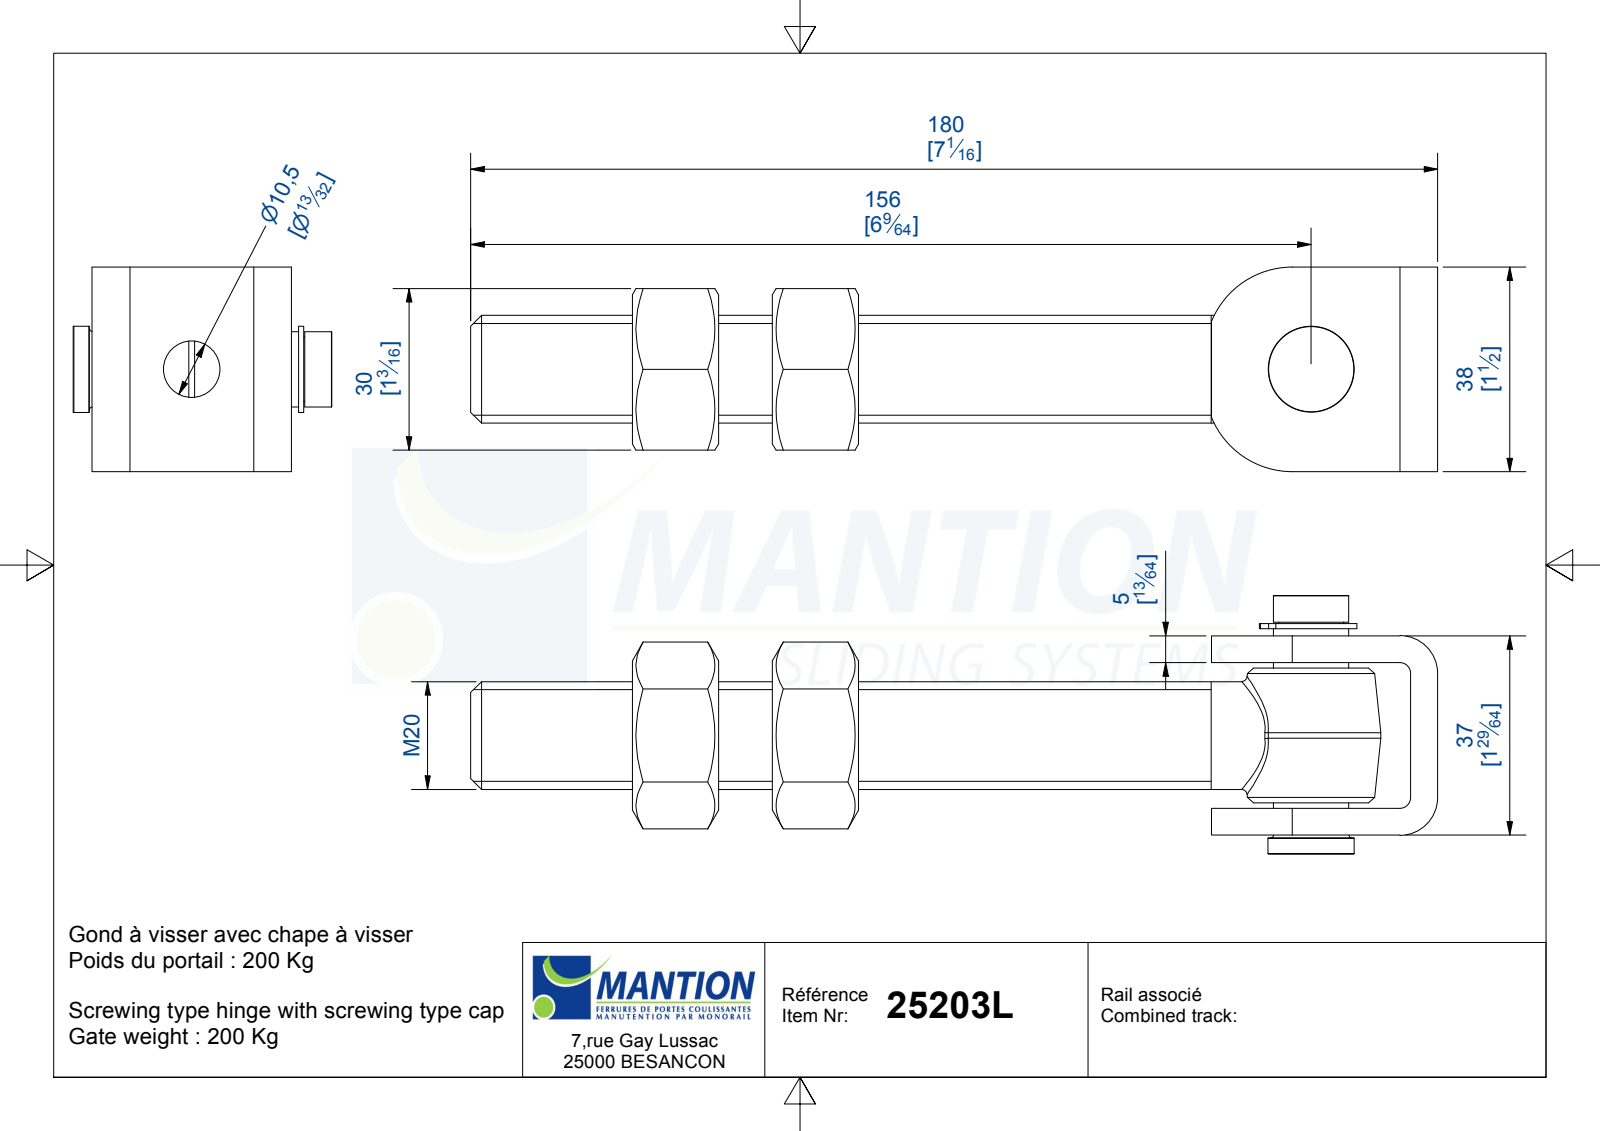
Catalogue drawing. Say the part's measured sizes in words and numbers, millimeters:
The part is named "25203L; 25203-2; 25203-3; 25203L-1 (+2 more)". Its 3-D file was written by "Autodesk Inventor 2019 (AUTOMOTIVE_DESIGN)". It is 6 solids with 157 faces: 40 planar, 88 cylindrical and 29 other. Overall it measures 179.5 by 48 by 38 millimeters. Its volume is 85 223 cubic millimeters and its surface area 38 142 square millimeters. Round holes: 2 of diameter 1.5, 1 of diameter 10.5, 1 of diameter 12.4, 1 of diameter 14.1, 1 of diameter 14.2, 1 of diameter 17.29. Round bosses or shafts: 2 of diameter 16, 1 of diameter 20, 1 of diameter 14, 1 of diameter 12. Partial cylindrical surfaces (rounded edges, fillets, slot ends): 4 of radius 1.5, 2 of radius 2, 2 of radius 7, 2 of radius 16.25, 1 of radius 9.6, 1 of radius 10.1. The main face-to-face distances are 5, 32, 30, 37, 27, 26, 4, 34, 16, 1. The hole center spacings are 8.1, 3.
